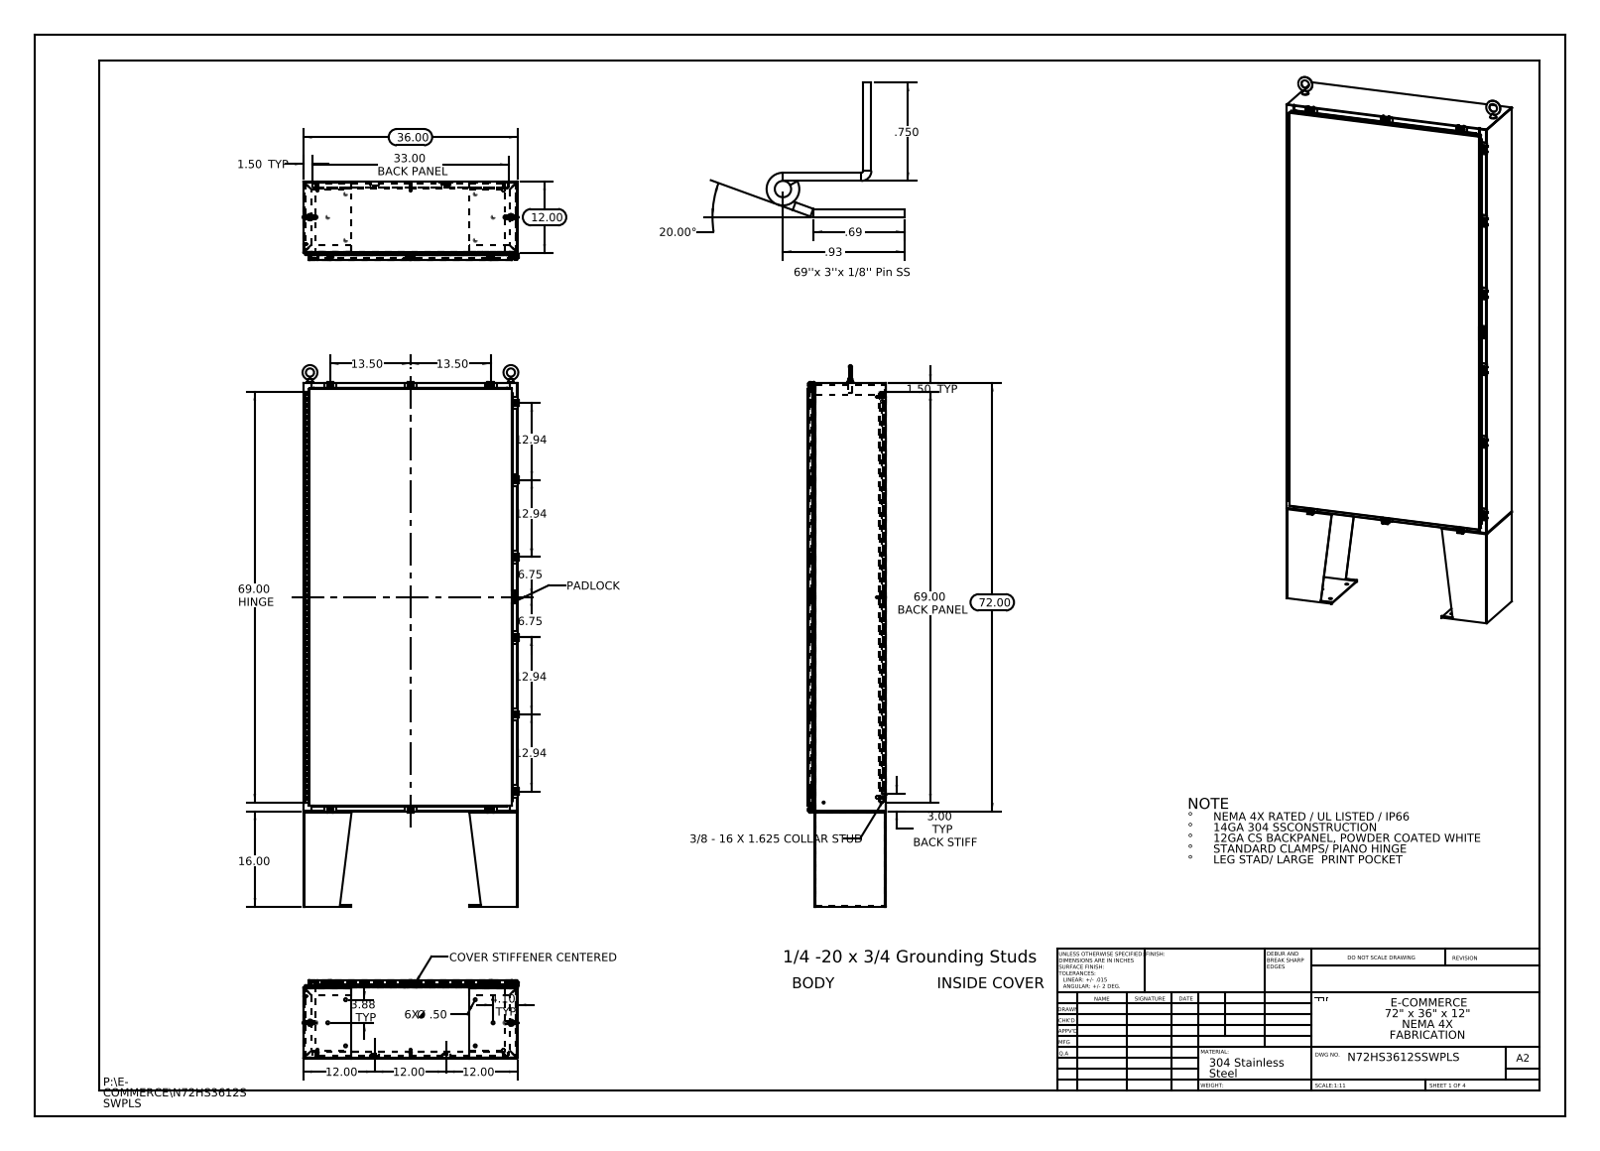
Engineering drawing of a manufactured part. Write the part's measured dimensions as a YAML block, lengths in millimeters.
part_name: "N72HS3612SSWPLS Cover; N72HS3612SSWPLS Door Stiffener; N72HS3612SSWPLS 22101002; N72HS3612SSWPLS Padlock Staple (+8 more)"
step_written_by: "SolidWorks 2013 (CONFIG_CONTROL_DESIGN)"
units: millimeters
bodies: {solids: 98, faces: 4079, planar: 2076, cylindrical: 1711, other: 292}
overall_size: [2311.4, 923.2, 335.3]
volume: 17480000
surface_area: 16650000
round_holes:
  - {diameter: 12.7, count: 14}
  - {diameter: 5.4, count: 12}
  - {diameter: 6.6, count: 12}
  - {diameter: 6.4, count: 8}
  - {diameter: 19.1, count: 4}
  - {diameter: 3.2, count: 2}
  - {diameter: 3.2, count: 1}
round_bosses_or_shafts:
  - {diameter: 6.4, count: 13}
  - {diameter: 12.7, count: 12}
  - {diameter: 10.1, count: 12}
  - {diameter: 15.9, count: 10}
  - {diameter: 9.5, count: 8}
  - {diameter: 8.4, count: 8}
  - {diameter: 4, count: 8}
  - {diameter: 3.6, count: 8}
partial_cylinders:
  - {radius: 1.5, count: 54}
  - {radius: 0.3, count: 39}
  - {radius: 2.2, count: 33}
  - {radius: 3, count: 24}
  - {radius: 3.6, count: 24}
  - {radius: 1.3, count: 19}
  - {radius: 2, count: 18}
  - {radius: 2.3, count: 18}
face_to_face_distances: [1.9, 333.4, 2.6, 331.5, 27.3, 335.3, 308, 25.4, 306.1, 29.9]
hole_center_spacings: [342.9, 56.5, 181.3, 347, 637.4, 854.1, 909, 941.8]
